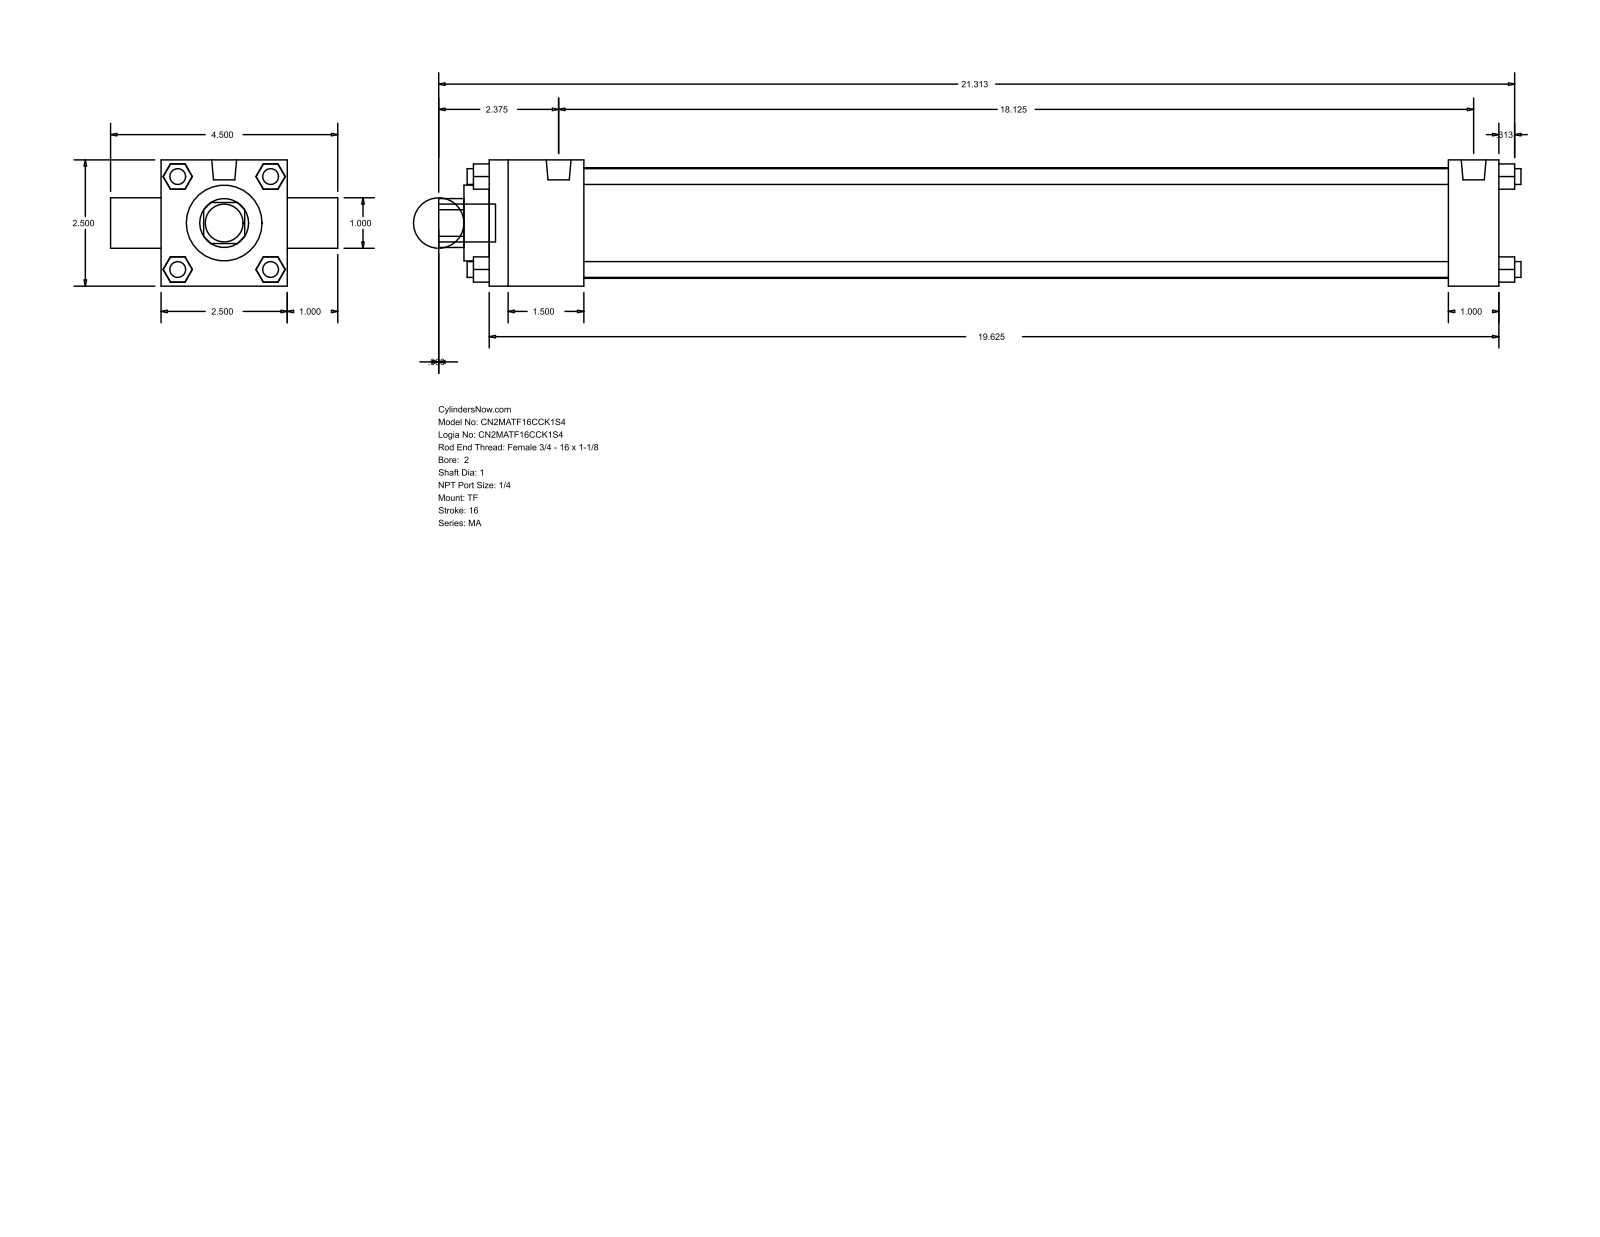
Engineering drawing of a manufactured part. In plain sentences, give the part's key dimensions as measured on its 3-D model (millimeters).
The part is named "MA_TF__0200_1". Its 3-D file was written by "GSSL Pune (CONFIG_CONTROL_DESIGN)". It is 0 solids with 120 faces: 92 planar, 28 cylindrical and 0 other. Overall it measures 544.51 by 114.3 by 63.5 millimeters. Round holes: 2 of diameter 25.4, 1 of diameter 38.1, 1 of diameter 55.63. Round bosses or shafts: 7 of diameter 7.94, 2 of diameter 12.49, 1 of diameter 19.05. Partial cylindrical surfaces (rounded edges, fillets, slot ends): 1 of radius 12.29. The main face-to-face distances are 63.5, 25.4, 508, 12.7, 47.63, 482.6, 434.97, 460.37, 88.9, 40.47.
